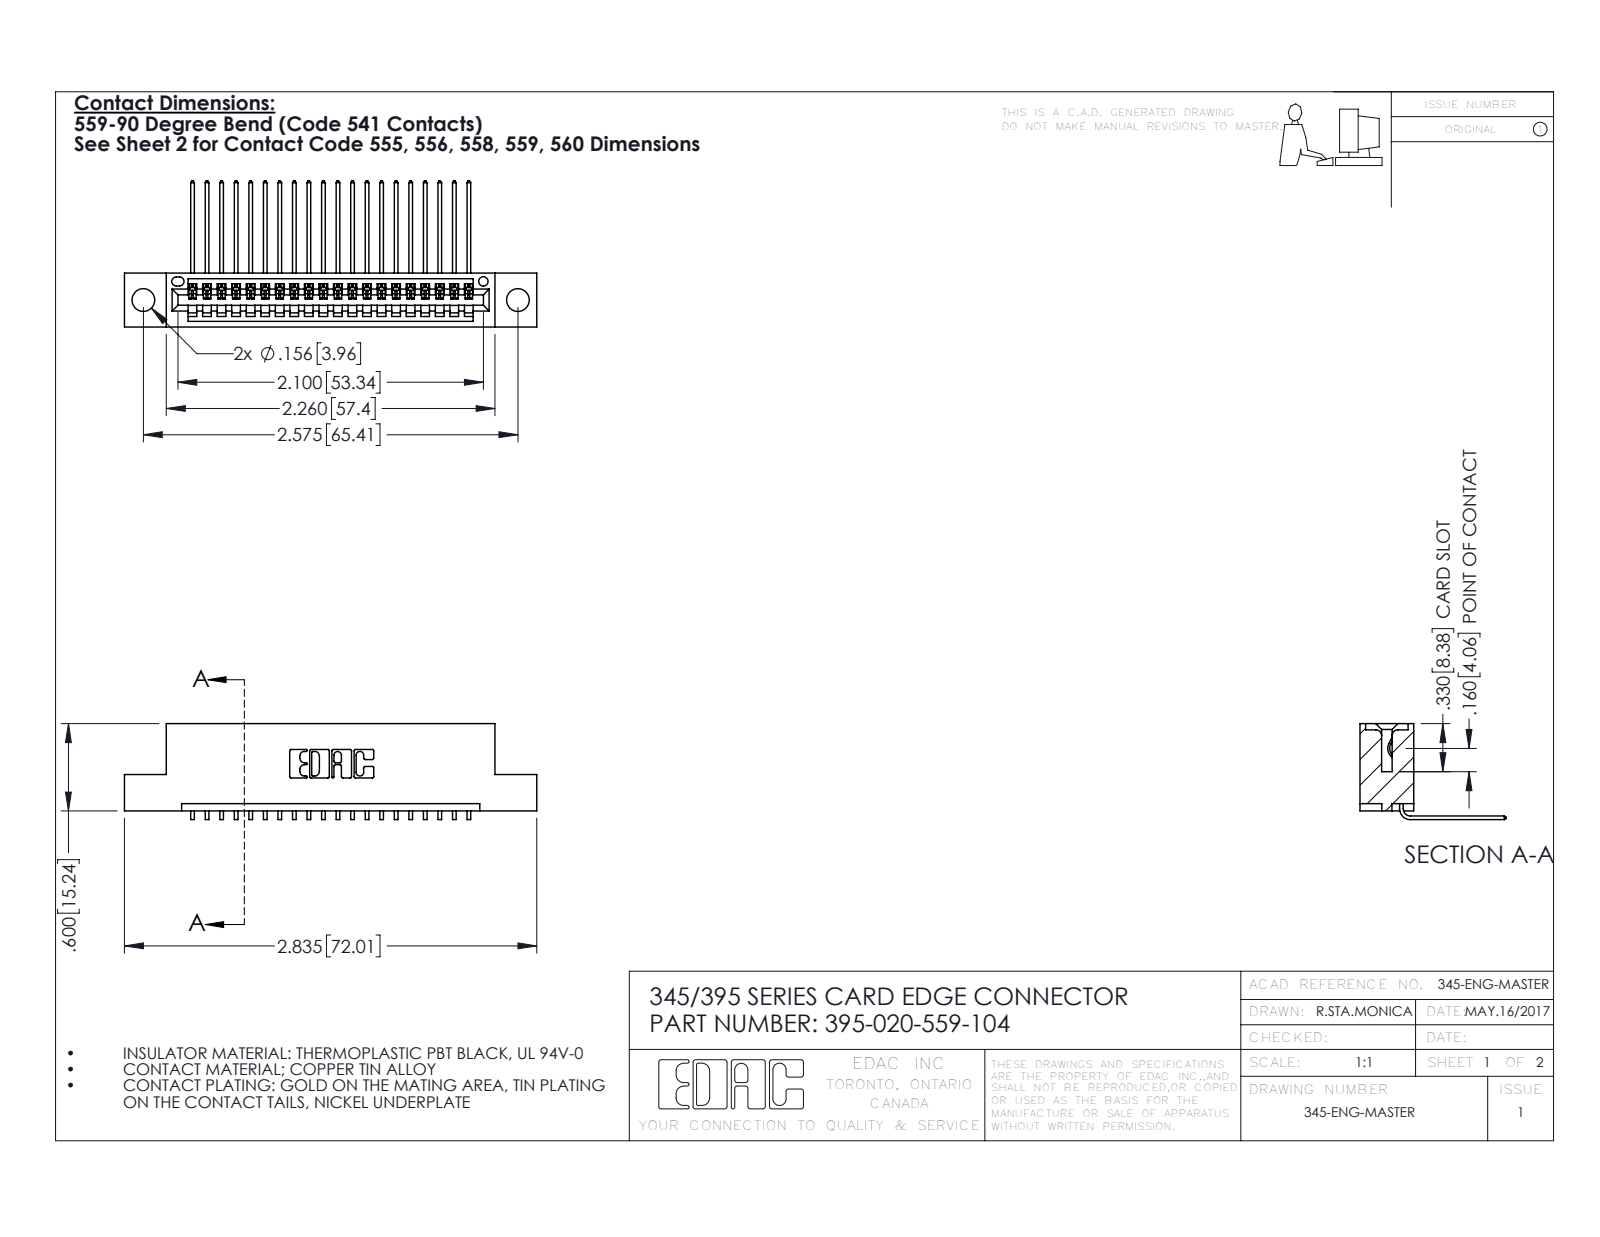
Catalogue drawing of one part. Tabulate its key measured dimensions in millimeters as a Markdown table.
| quantity | value |
| --- | --- |
| part name | 345-292-001_558 559 Tail - 1; 345 Part_Flush Mounting Lugs - 0.156 Dia-TH; 395-020-559-104 |
| STEP written by | SolidWorks 2016 (CONFIG_CONTROL_DESIGN) |
| units | millimeters |
| bodies | 21 solids, 1326 faces (920 planar, 406 cylindrical, 0 other) |
| overall size | 72 × 25.5 × 16.7 |
| volume | 6 640 mm³ |
| surface area | 8 723 mm² |
| round holes (diameter × count) | 4 × 2, 1.6 × 1 |
| partial cylindrical surfaces (radius × count) | 0.2 × 40, 0.3 × 22, 0.2 × 6, 0.8 × 6, 0.7 × 3, 0.8 × 2, 1 × 2, 0.4 × 1 |
| main face-to-face distances | 7.6, 1.8, 5.1, 9.4, 2.5, 6.9, 0.6, 5.7, 3.8, 15.2 |
| hole center spacings | 6.9, 59.5, 65.4 |
